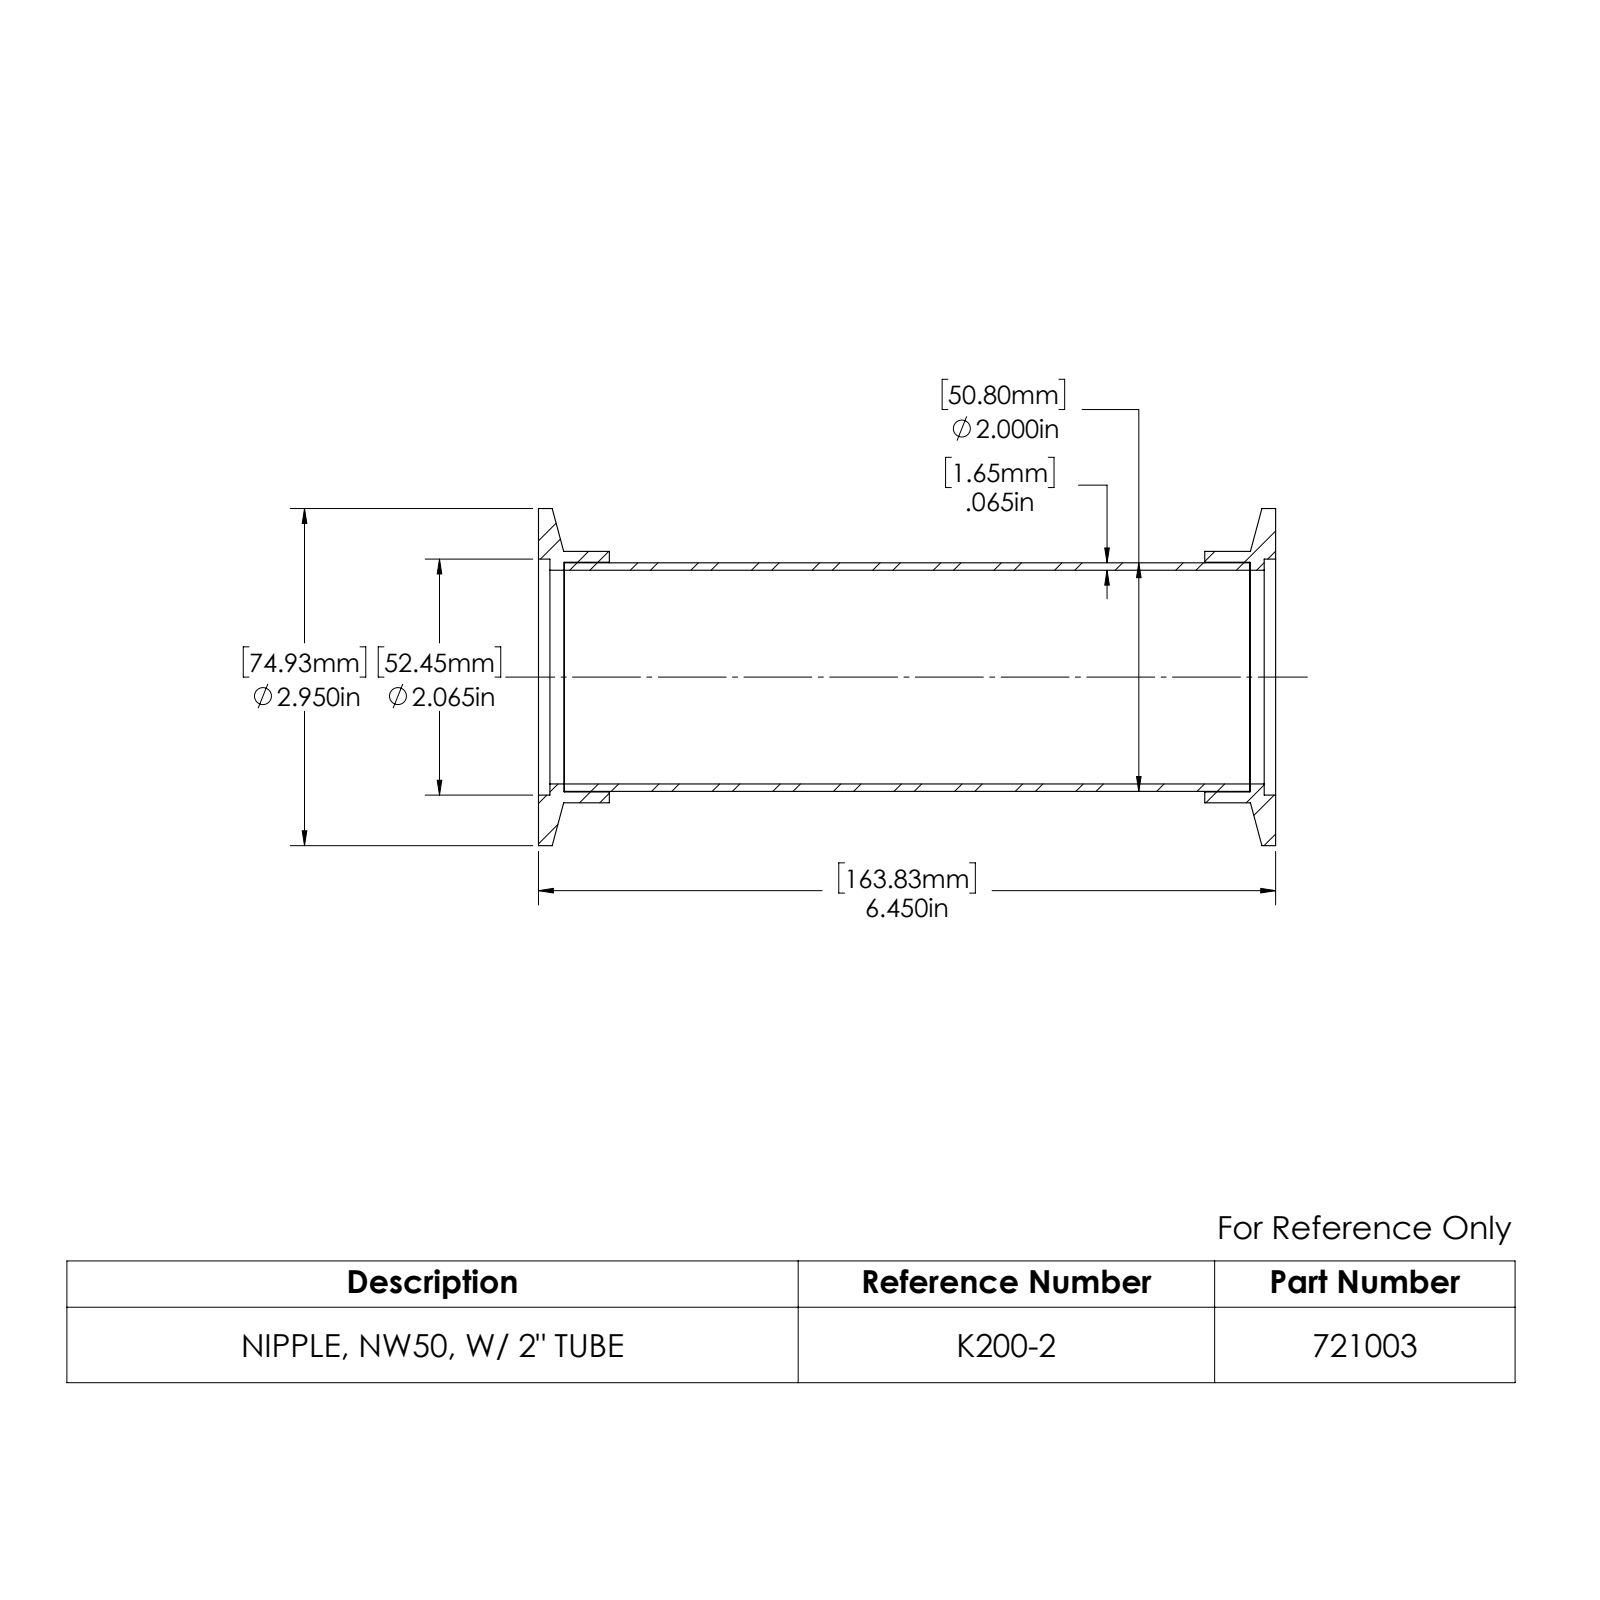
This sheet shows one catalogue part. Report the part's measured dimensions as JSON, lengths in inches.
{"part_name": "721003; 940203; 713004", "step_written_by": "SolidWorks 2022 (AUTOMOTIVE_DESIGN)", "units": "inches", "bodies": {"solids": 3, "faces": 38, "planar": 10, "cylindrical": 24, "other": 4}, "overall_size": [6.45, 2.95, 2.95], "volume_in3": 4.239, "surface_area_in2": 105.8, "round_holes": [[1.87, 1], [2.01, 1], [2.065, 1]], "round_bosses_or_shafts": [[2.95, 1], [2.2, 1], [2, 1]], "face_to_face_distances": [6.45, 0.395, 5.605, 0.1, 6.35, 0.225, 6.225, 6, 6.225, 0.225]}
